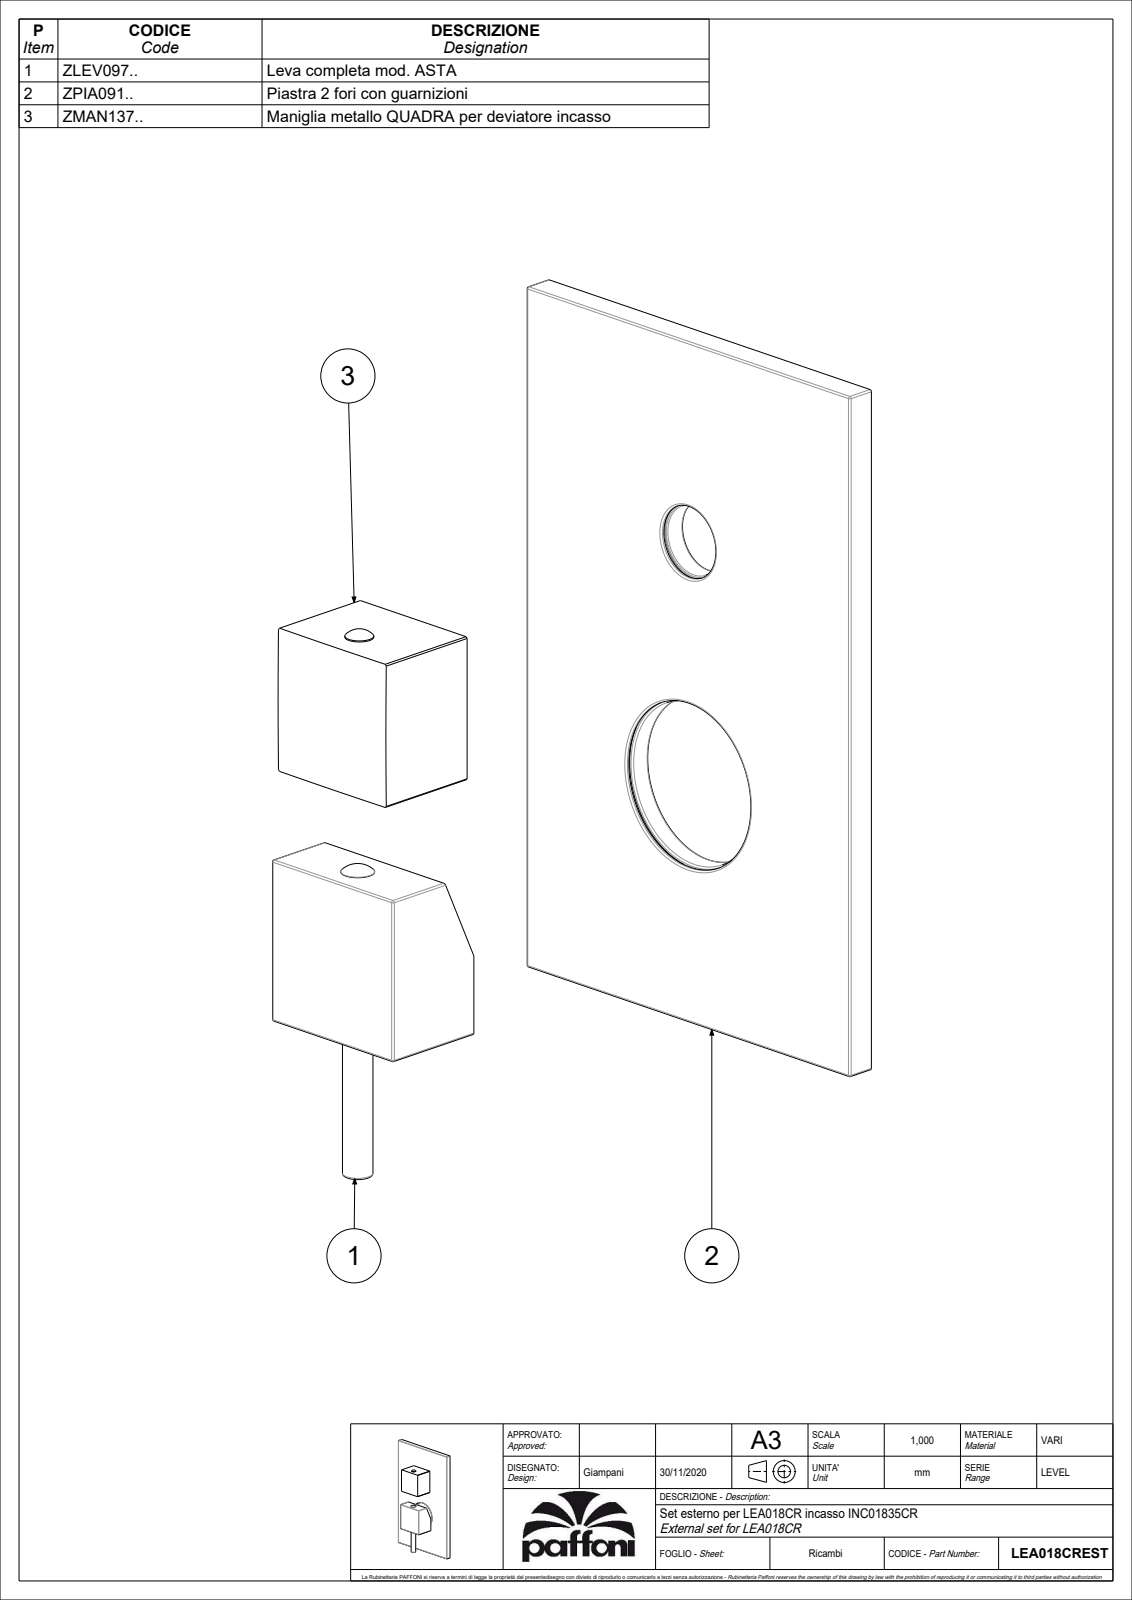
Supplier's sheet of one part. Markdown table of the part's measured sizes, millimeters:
| quantity | value |
| --- | --- |
| part name | LEA018CREST |
| STEP written by | CREO PARAMETRIC BY PTC INC, 2020044 (CONFIG_CONTROL_DESIGN) |
| units | millimeters |
| bodies | 3 solids, 298 faces (130 planar, 102 cylindrical, 66 other) |
| overall size | 190 × 120 × 40.49 |
| volume | 158 643 mm³ |
| surface area | 105 795 mm² |
| round holes (diameter × count) | 5.5 × 2, 3 × 1, 3.2 × 1, 4.2 × 1, 6 × 1, 8.1 × 1, 14.8 × 1, 19.2 × 1, 20 × 1, 21 × 1, 23.2 × 1, 36 × 1 |
| round bosses / shafts (diameter × count) | 5 × 2, 51 × 1, 49 × 1, 25 × 1, 23 × 1, 8 × 1, 7.6 × 1 |
| partial cylindrical surfaces (radius × count) | 0.5 × 18, 1 × 8, 28 × 1 |
| main face-to-face distances | 2.5, 5.5, 8, 3, 0.5, 5, 40, 32, 2, 37.5 |
| hole center spacings | 0.6, 10, 58, 68 |
